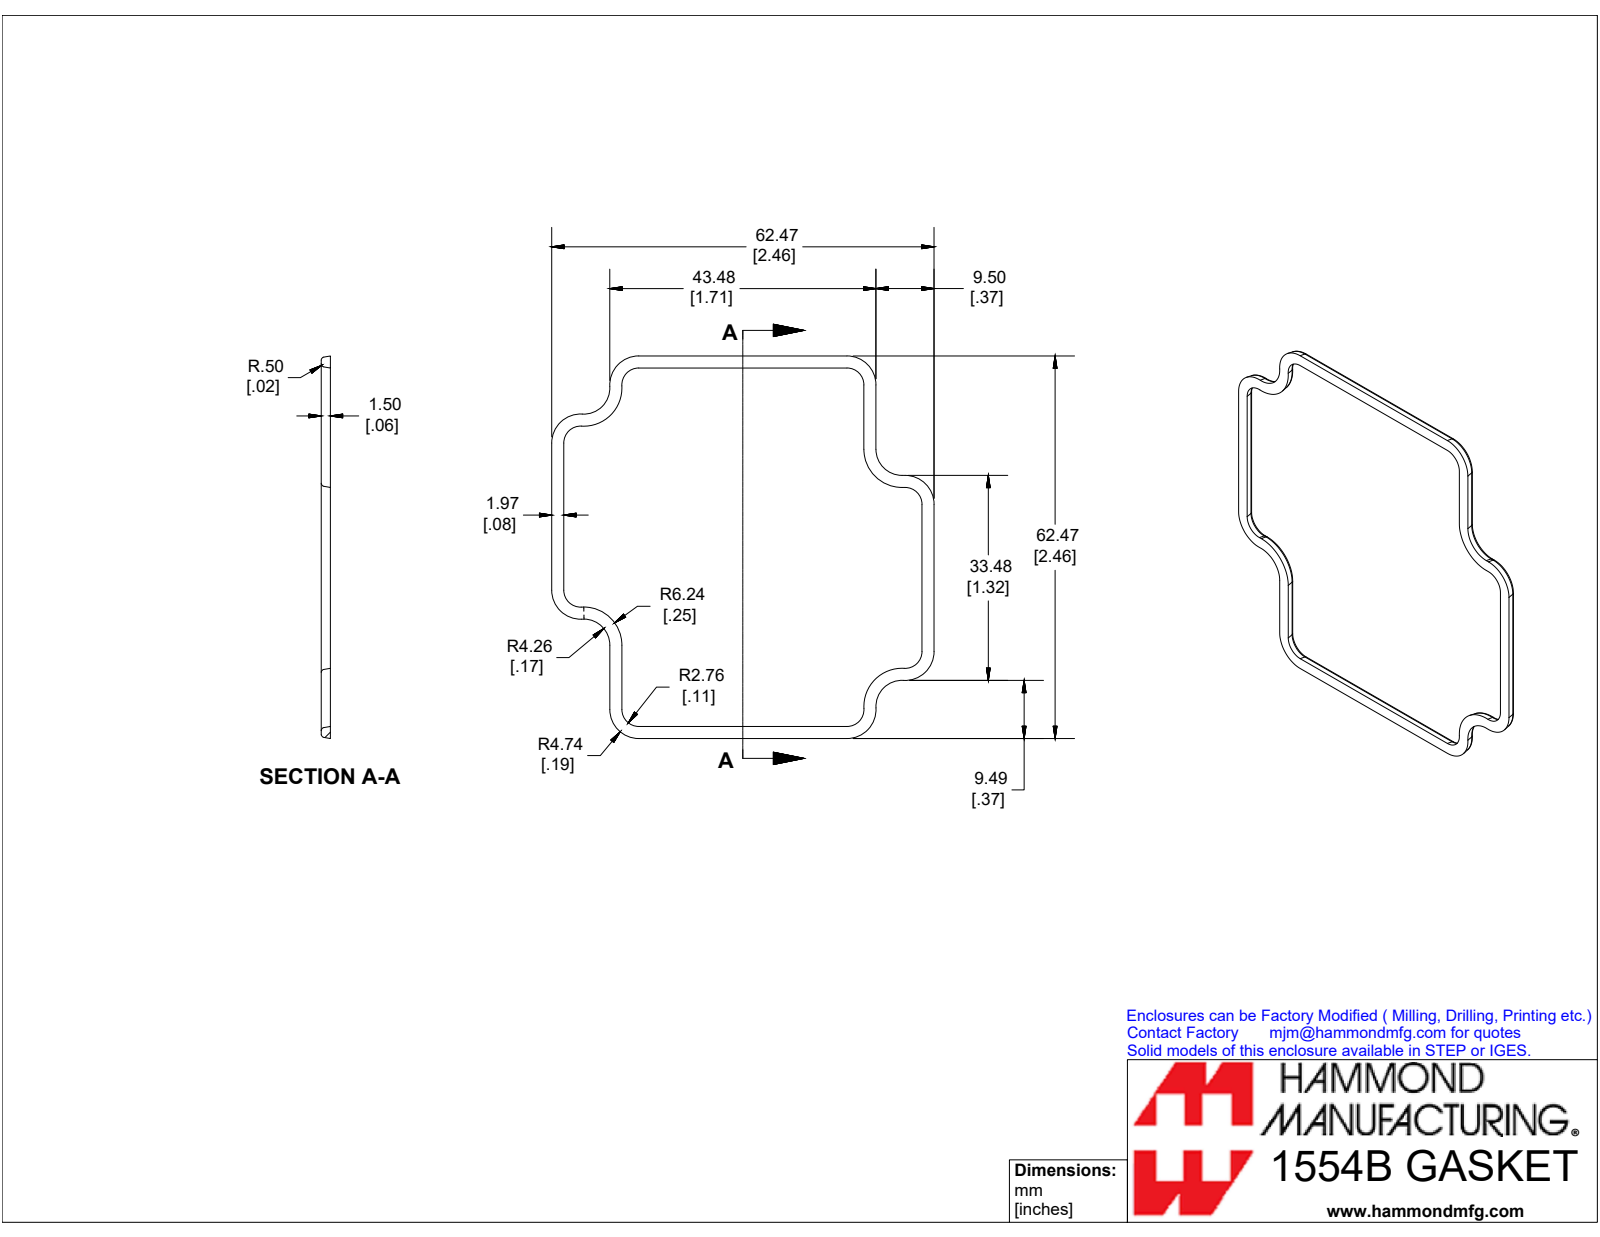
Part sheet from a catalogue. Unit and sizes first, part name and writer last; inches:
Units: inches
Overall size (bounding box): 2.459 × 2.459 × 0.059
Partial cylindrical surfaces — rounded edges, fillets, slot ends (radius × count): R0.02 ×16
Main face-to-face distances: 0.059, 2.346, 0.369, 1.978, 1.978, 0.368, 1.609, 1.609, 1.59, 0.756
Volume: 0.033 in³ · Surface area: 2.108 in²
Bodies: 1 solid, 82 faces (18 planar, 16 cylindrical, 48 other)
Part name (STEP PRODUCT): 1554BGASKET
STEP written by: SolidWorks 2019 (CONFIG_CONTROL_DESIGN)
